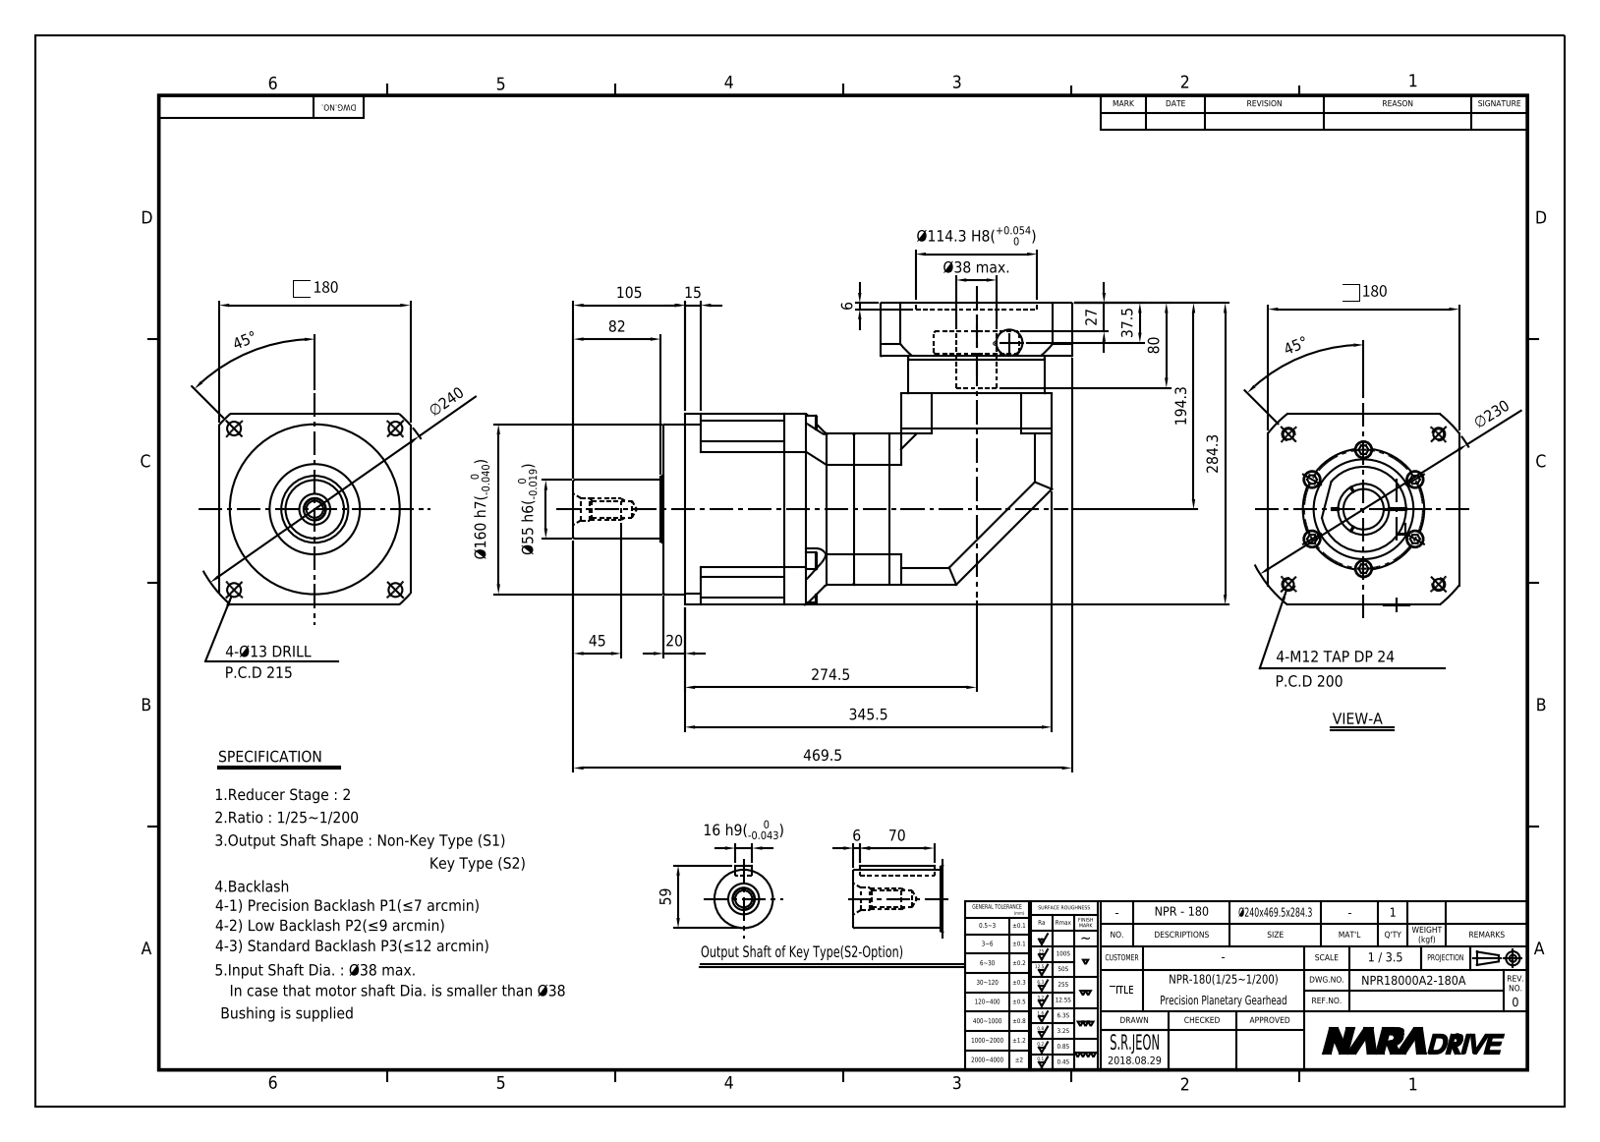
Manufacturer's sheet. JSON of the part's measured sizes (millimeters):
{"part_name": "NPR18000A2-180A-S1", "step_written_by": "Autodesk Inventor 2015 (AUTOMOTIVE_DESIGN)", "units": "millimeters", "bodies": {"solids": 2, "faces": 777, "planar": 365, "cylindrical": 212, "other": 200}, "overall_size": [469.5, 284.3, 181], "volume_mm3": 8078000, "surface_area_mm2": 628930, "round_holes": [[6.65, 18], [14, 18], [8.5, 12], [9, 6], [8.38, 5], [11, 5], [10.11, 4], [13, 4], [12.5, 1], [14.5, 1], [17.29, 1], [21, 1]], "round_bosses_or_shafts": [[13, 14], [8, 14], [16, 5], [10, 5], [128, 1], [80, 1], [63, 1], [55, 1]], "partial_cylinders_radius": [[5, 8], [15, 8], [0.5, 4], [1, 4], [3.32, 4], [82.5, 2], [9, 1], [57.15, 1]], "face_to_face_distances": [19, 161, 180, 142, 50, 101, 54.3, 104.3, 234.3, 284.3], "hole_center_spacings": [72.5, 56, 102.53, 115.83, 117.53, 178.52, 88.88, 113.04]}
